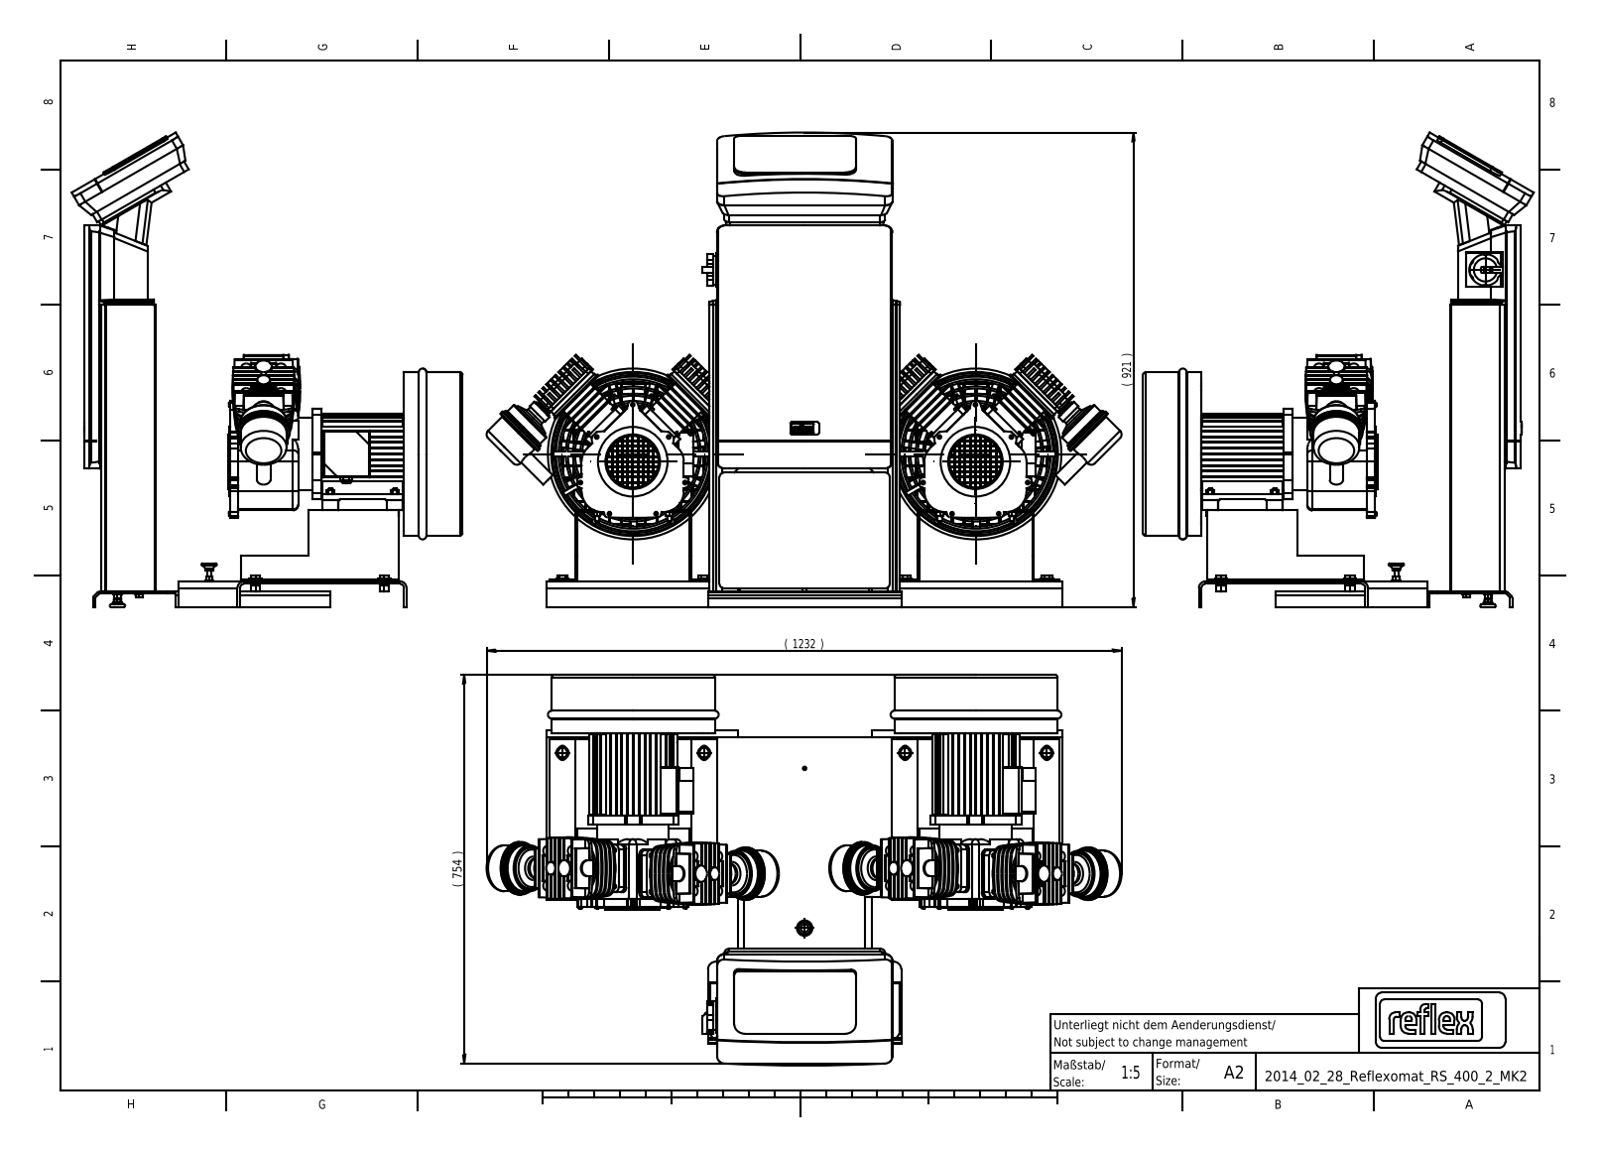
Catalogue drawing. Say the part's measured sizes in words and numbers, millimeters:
Its 3-D file was written by "Mechanical Desktop 2011 (CONFIG_CONTROL_DESIGN)". It is 130 solids with 8174 faces: 3780 planar, 1550 cylindrical and 2844 other. Overall it measures 1232.31 by 920.68 by 758.35 millimeters. Its volume is 53 720 000 cubic millimeters and its surface area 6 817 000 square millimeters. Round holes: 28 of diameter 7, 13 of diameter 17.5, 10 of diameter 10.5, 8 of diameter 13, 8 of diameter 17, 6 of diameter 5.5, 4 of diameter 9, 4 of diameter 13.5, 3 of diameter 5.4, 3 of diameter 20.5, 3 of diameter 23, 2 of diameter 6.65. Round bosses or shafts: 21 of diameter 8, 14 of diameter 7, 13 of diameter 16, 12 of diameter 20, 10 of diameter 19, 9 of diameter 11.2, 9 of diameter 5.1, 8 of diameter 30. Partial cylindrical surfaces (rounded edges, fillets, slot ends): 54 of radius 10, 45 of radius 1, 28 of radius 5, 25 of radius 3, 12 of radius 2, 12 of radius 4.25, 12 of radius 6.5, 10 of radius 4.5. The main face-to-face distances are 5, 3, 15, 159, 4, 19, 24, 20, 589.67, 135. The hole center spacings are 665, 45, 81.87, 31, 25.36, 68.02, 89.08, 62.
